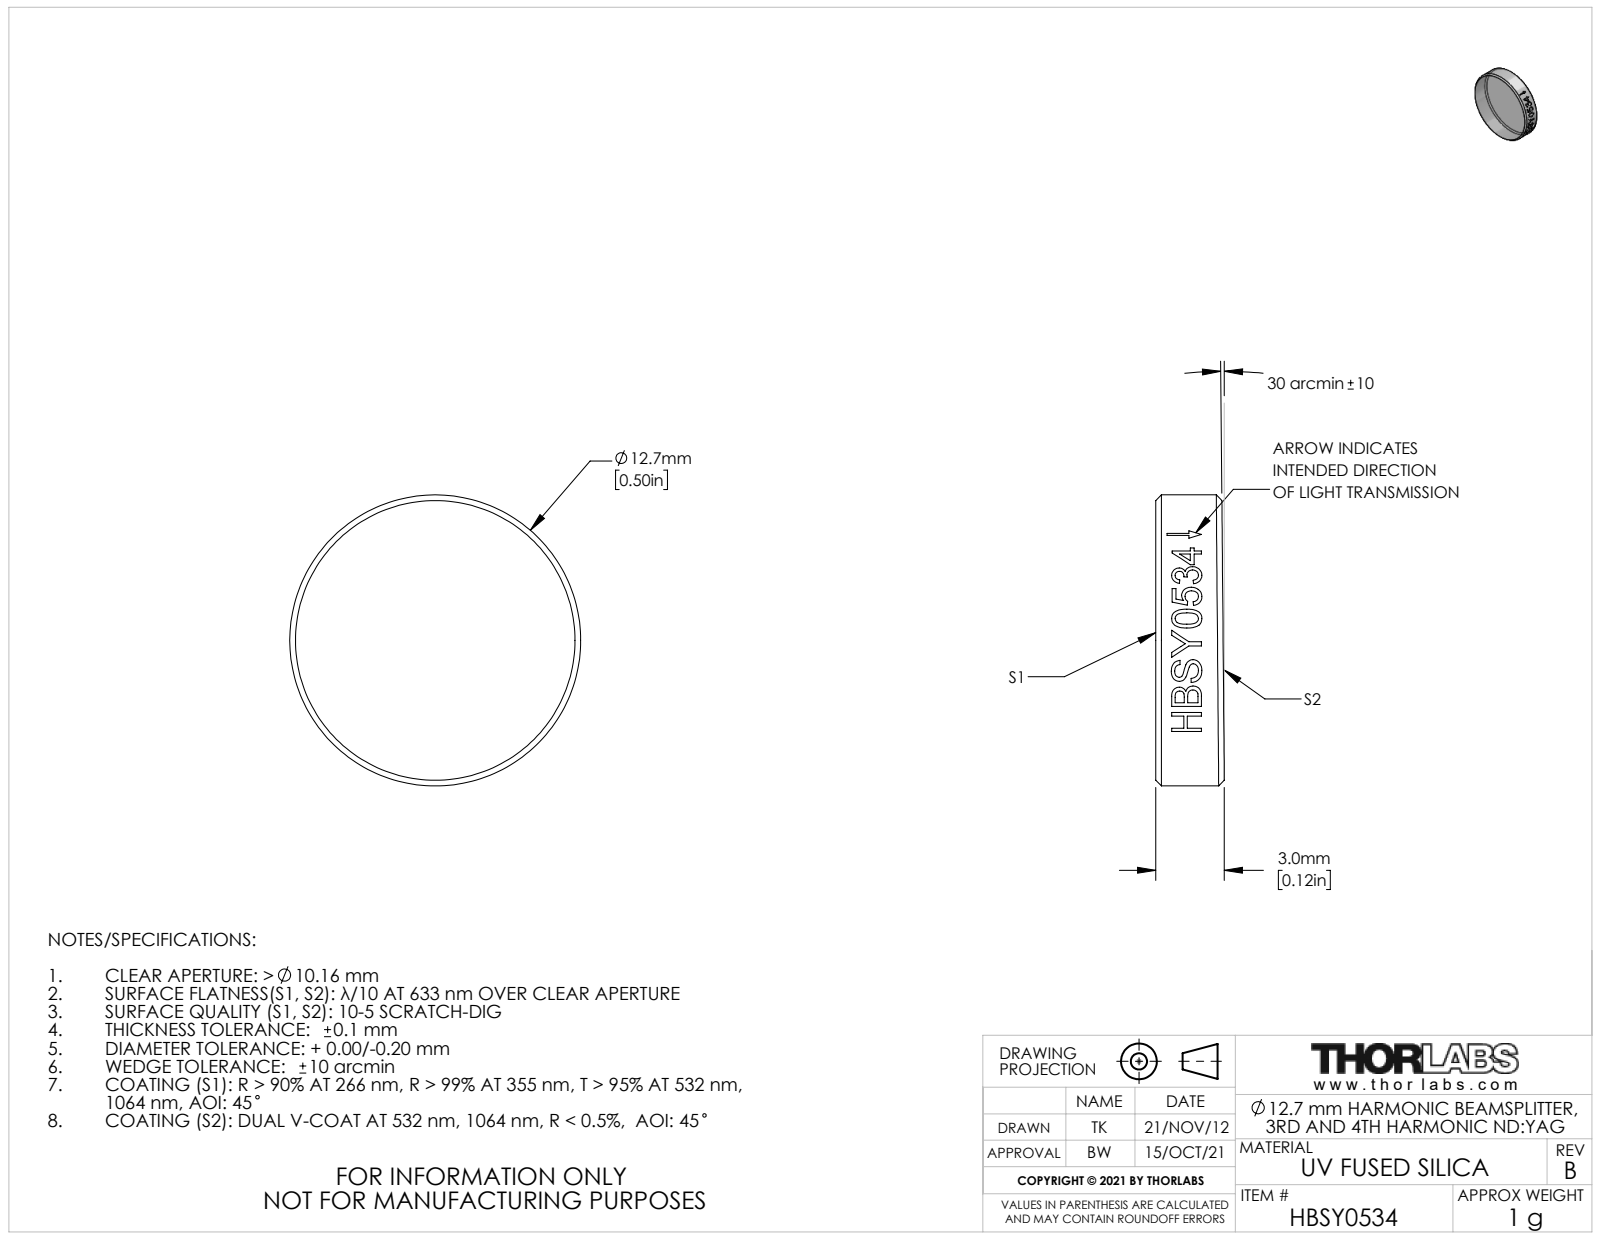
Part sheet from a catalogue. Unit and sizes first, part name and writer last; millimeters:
Units: millimetres
Overall size (bounding box): 12.7 × 12.7 × 3
Round bosses / shafts (diameter × count): ⌀12.7 ×1
Volume: 370 mm³ · Surface area: 359 mm²
Bodies: 1 solid, 21 faces (2 planar, 15 cylindrical, 4 other)
Part name (STEP PRODUCT): TTN006421-E0W
STEP written by: SolidWorks 2012 (CONFIG_CONTROL_DESIGN)
